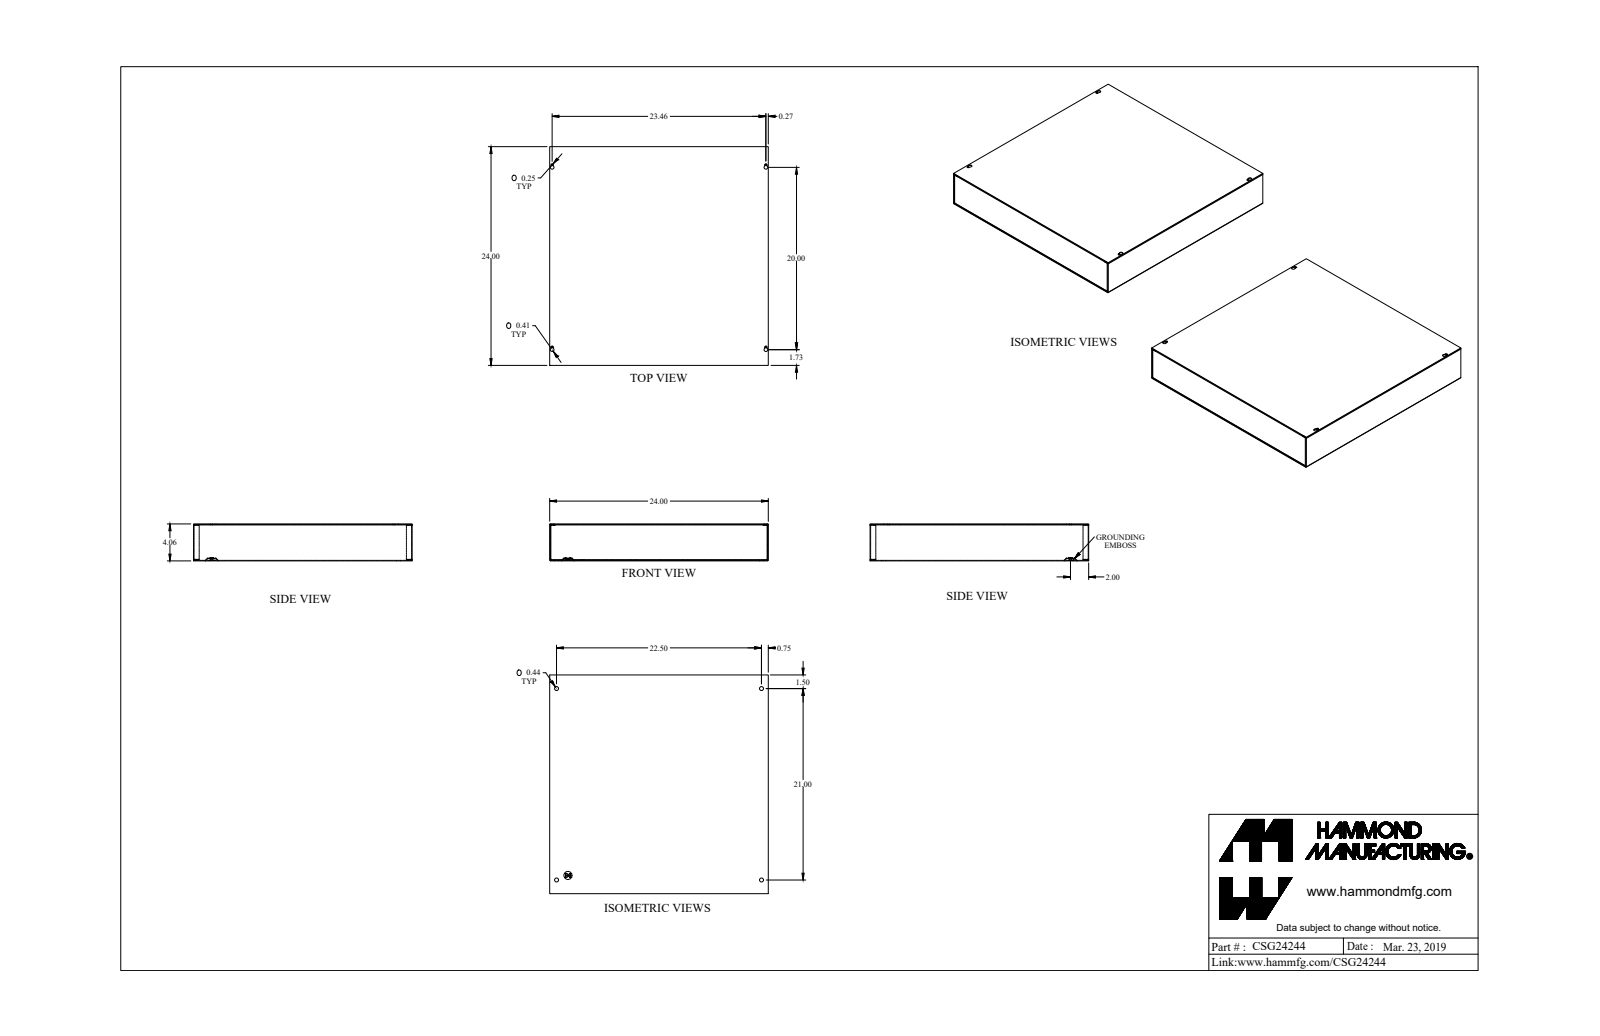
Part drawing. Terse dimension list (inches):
name: CSG24244_Default
written by: SolidWorks 2019 (CONFIG_CONTROL_DESIGN)
unit: in
bodies: 4 solids, 205 faces (125 planar, 72 cylindrical, 8 other)
size: 24 × 24 × 4.057
volume: 91.14 in³; area: 3 218 in²
holes: 5× ⌀0.17, 4× ⌀0.437, 1× ⌀0.5
bosses: 1× ⌀0.492, 1× ⌀0.284
rounds: 12× R0.029, 12× R0.086, 8× R0.057, 4× R0.125, 4× R0.203
face distances: 0.057, 4, 3.943, 4.057, 23.943, 24, 23.886, 0.08, 3.863, 3.92
hole spacings: 0.693, 20.506, 22.985, 30.795, 20, 21, 22.5, 23.46
